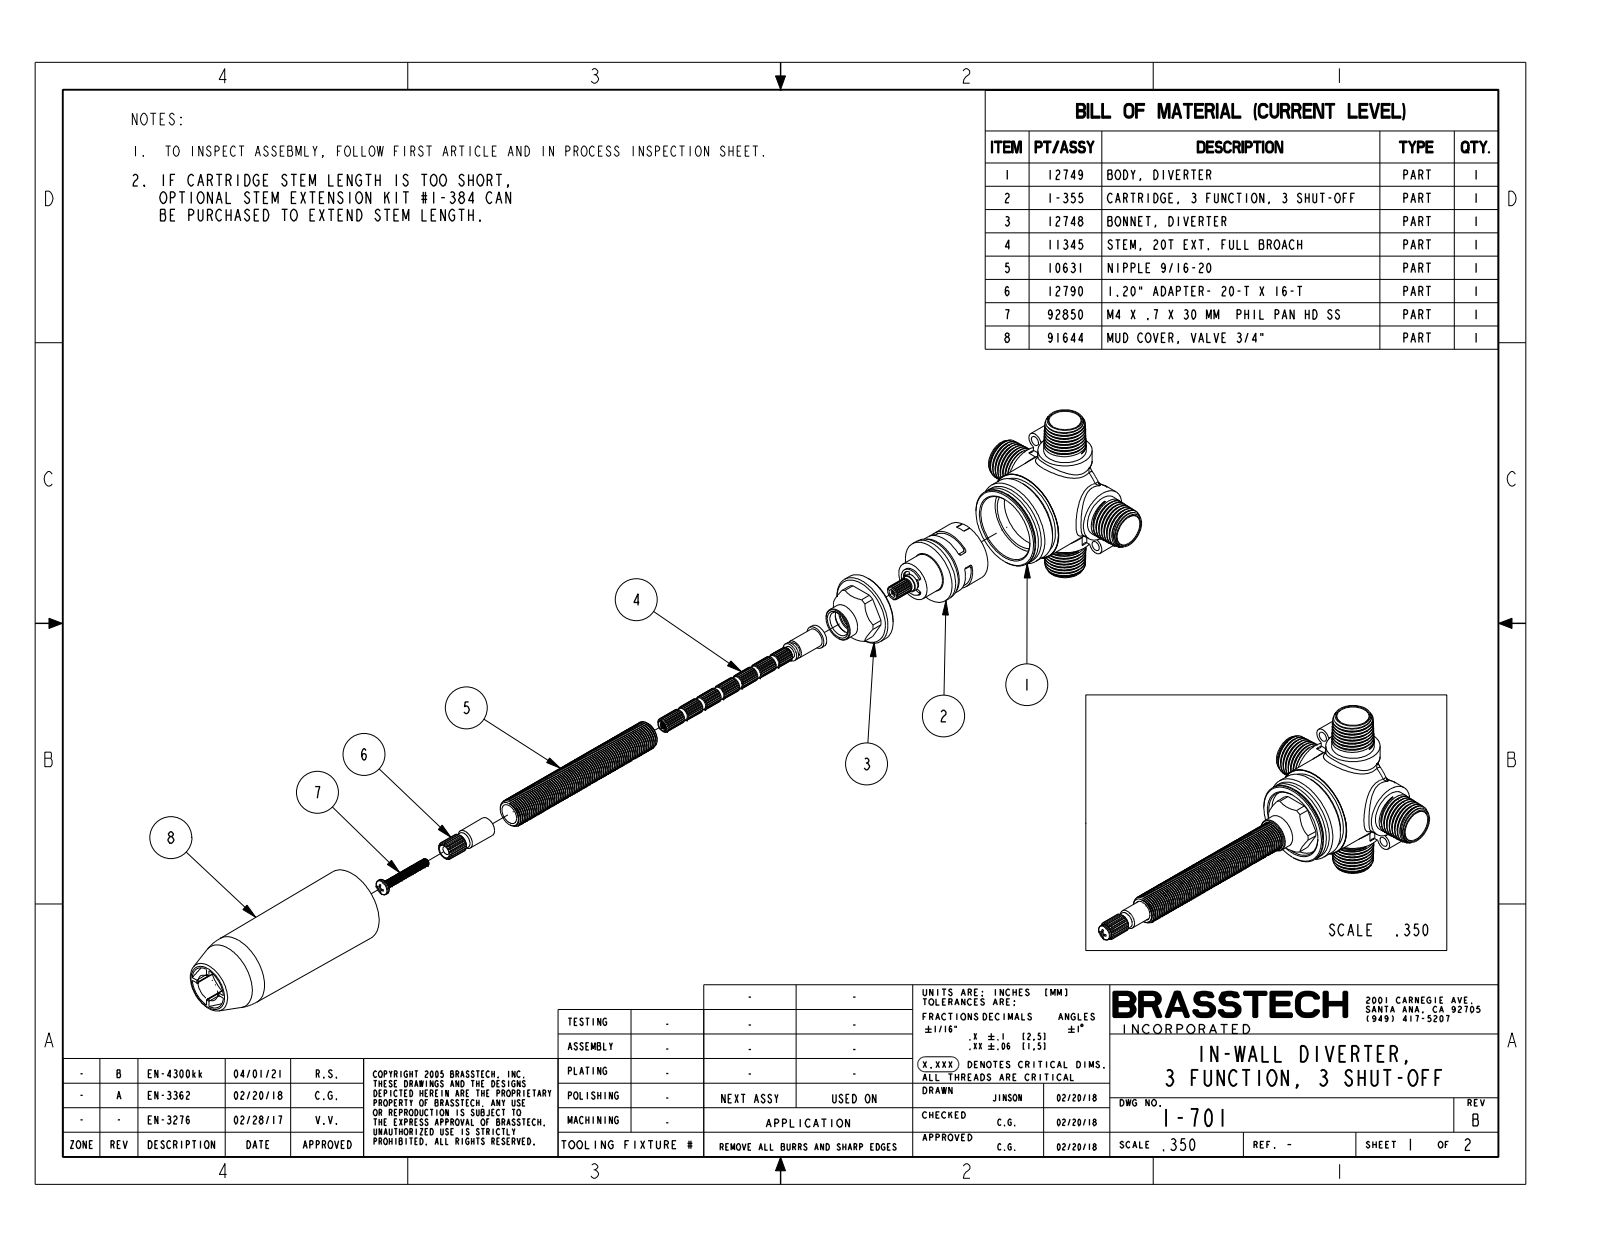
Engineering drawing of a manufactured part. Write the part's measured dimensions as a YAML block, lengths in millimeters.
part_name: "1-701"
step_written_by: "CREO PARAMETRIC BY PTC INC, 2018400 (AUTOMOTIVE_DESIGN)"
units: millimeters
bodies: {solids: 1, faces: 924, planar: 174, cylindrical: 442, other: 308}
overall_size: [192.4, 90, 90]
volume: 120900
surface_area: 34630
round_holes:
  - {diameter: 5, count: 2}
  - {diameter: 10, count: 2}
  - {diameter: 14.9, count: 2}
  - {diameter: 16, count: 2}
  - {diameter: 4.4, count: 1}
  - {diameter: 8.4, count: 1}
  - {diameter: 45.8, count: 1}
round_bosses_or_shafts:
  - {diameter: 27, count: 2}
  - {diameter: 46, count: 1}
  - {diameter: 44, count: 1}
  - {diameter: 41.5, count: 1}
  - {diameter: 17, count: 1}
  - {diameter: 14.3, count: 1}
  - {diameter: 9.9, count: 1}
  - {diameter: 8.3, count: 1}
partial_cylinders:
  - {radius: 1.8, count: 13}
  - {radius: 4, count: 5}
  - {radius: 4.2, count: 2}
  - {radius: 6.2, count: 2}
  - {radius: 3.5, count: 1}
  - {radius: 4.2, count: 1}
  - {radius: 4.7, count: 1}
  - {radius: 13.9, count: 1}
face_to_face_distances: [49.5, 53, 4, 49, 0.5, 4.5, 53.5, 34.5, 15, 8.7]
hole_center_spacings: [30.3, 60.5]
